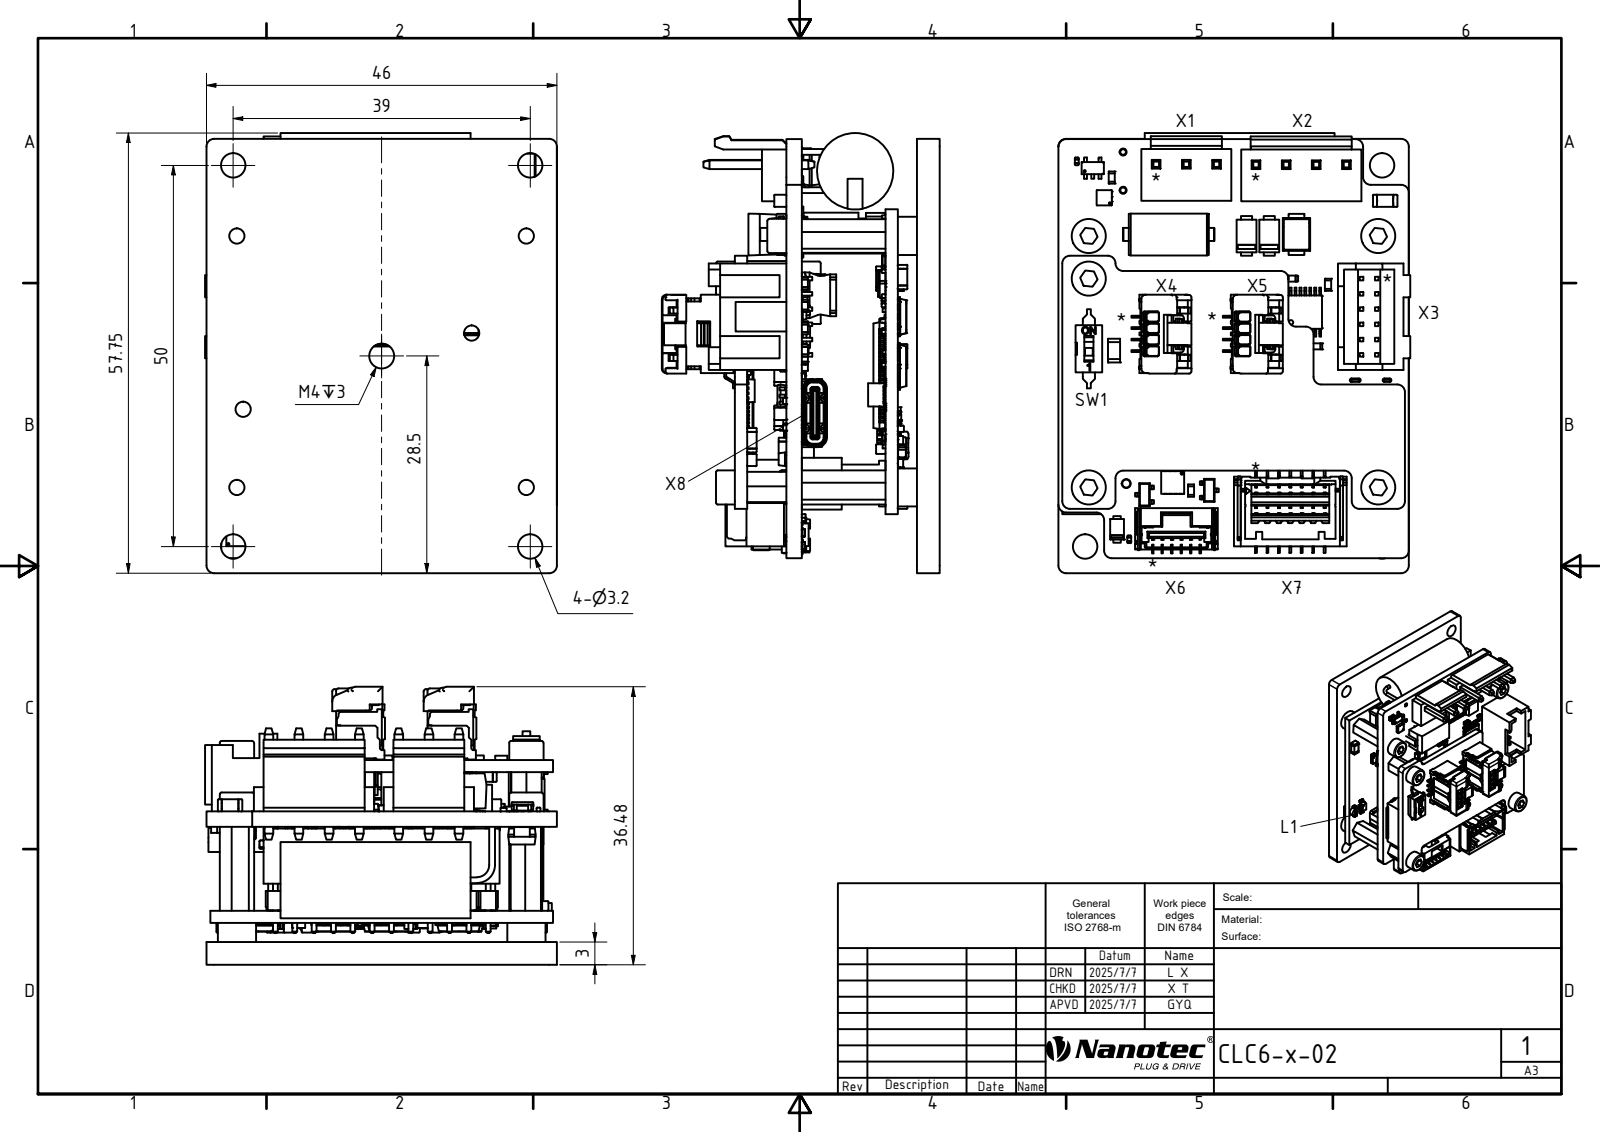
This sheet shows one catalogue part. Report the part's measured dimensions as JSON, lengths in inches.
{"part_name": "CLC6-x-02", "step_written_by": "Autodesk Inventor 2024 (AUTOMOTIVE_DESIGN)", "units": "inches", "bodies": {"solids": 0, "faces": 29825, "planar": 21720, "cylindrical": 5389, "other": 2716}, "overall_size": [2.274, 1.819, 1.436], "round_holes": [[0.036, 24], [0.028, 12], [0.067, 7], [0.079, 7], [0.012, 5], [0.024, 4], [0.099, 4], [0.102, 4], [0.126, 4], [0.01, 3], [0.106, 3], [0.035, 2]], "round_bosses_or_shafts": [[0.016, 8], [0.177, 5], [0.098, 5], [0.197, 4], [0.045, 4], [0.041, 4], [0.04, 4], [0.03, 4]], "partial_cylinders_radius": [[0.004, 1128], [0.008, 212], [0.006, 62], [0.008, 50], [0.005, 48], [0.039, 42], [0.012, 36], [0.005, 26]], "face_to_face_distances": [0.08, 0.713, 0.674, 0.118, 0.793, 0.595, 0.098, 0.217, 0.576, 0.496], "hole_center_spacings": [0.1, 0.2, 0.224, 0.141, 0.3, 0.316, 0.4, 0.412]}
